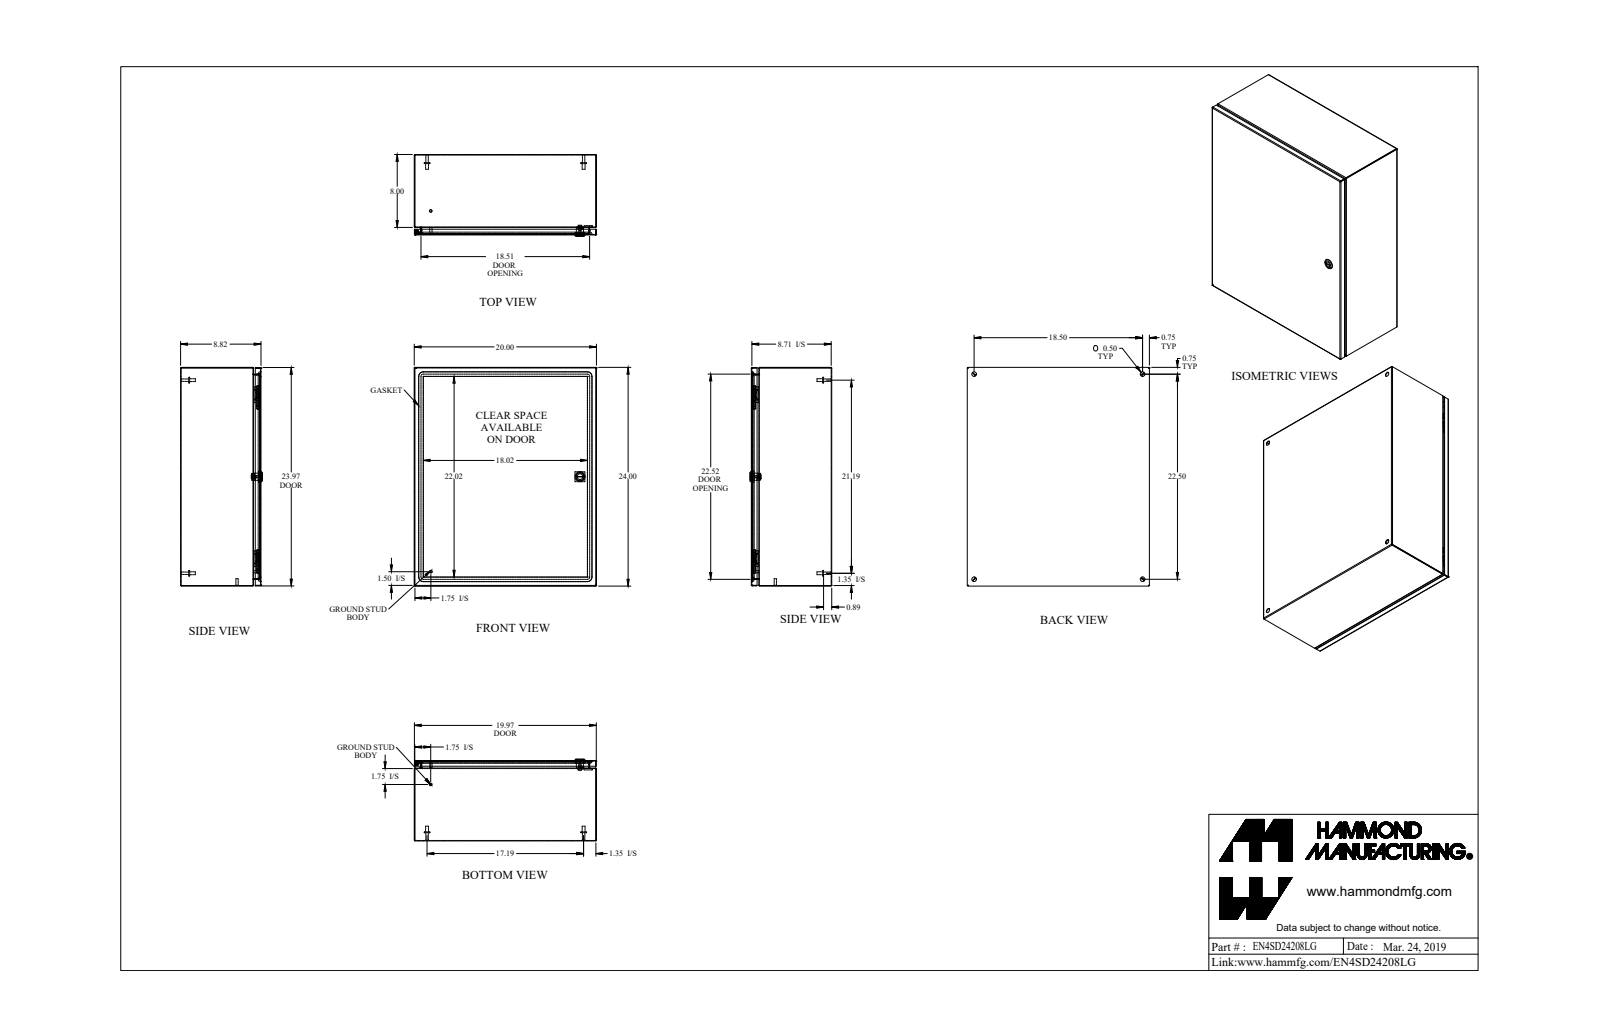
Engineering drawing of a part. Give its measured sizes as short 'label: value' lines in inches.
name: EN4SD24208LG_Default
written by: SolidWorks 2019 (CONFIG_CONTROL_DESIGN)
unit: in
bodies: 21 solids, 634 faces (285 planar, 213 cylindrical, 136 other)
size: 24 × 20 × 8.982
volume: 113.2 in³; area: 3 865 in²
holes: 4× ⌀0.5, 1× ⌀0.172, 1× ⌀0.232, 1× ⌀0.24, 1× ⌀0.242, 1× ⌀0.625, 1× ⌀0.785
bosses: 4× ⌀0.625, 4× ⌀0.313, 4× ⌀0.27, 2× ⌀0.281, 2× ⌀0.25, 1× ⌀1.1, 1× ⌀0.525, 1× ⌀0.455
rounds: 21× R0.029, 21× R0.086, 16× R0.25, 8× R19, 4× R0.006, 4× R0.062, 4× R0.499, 2× R0.125
face distances: 0.057, 8.765, 8.708, 8.822, 19.943, 23.943, 19.886, 20, 23.886, 24
hole spacings: 18.5, 22.5, 29.129, 11.299, 11.3, 20.754, 20.755
